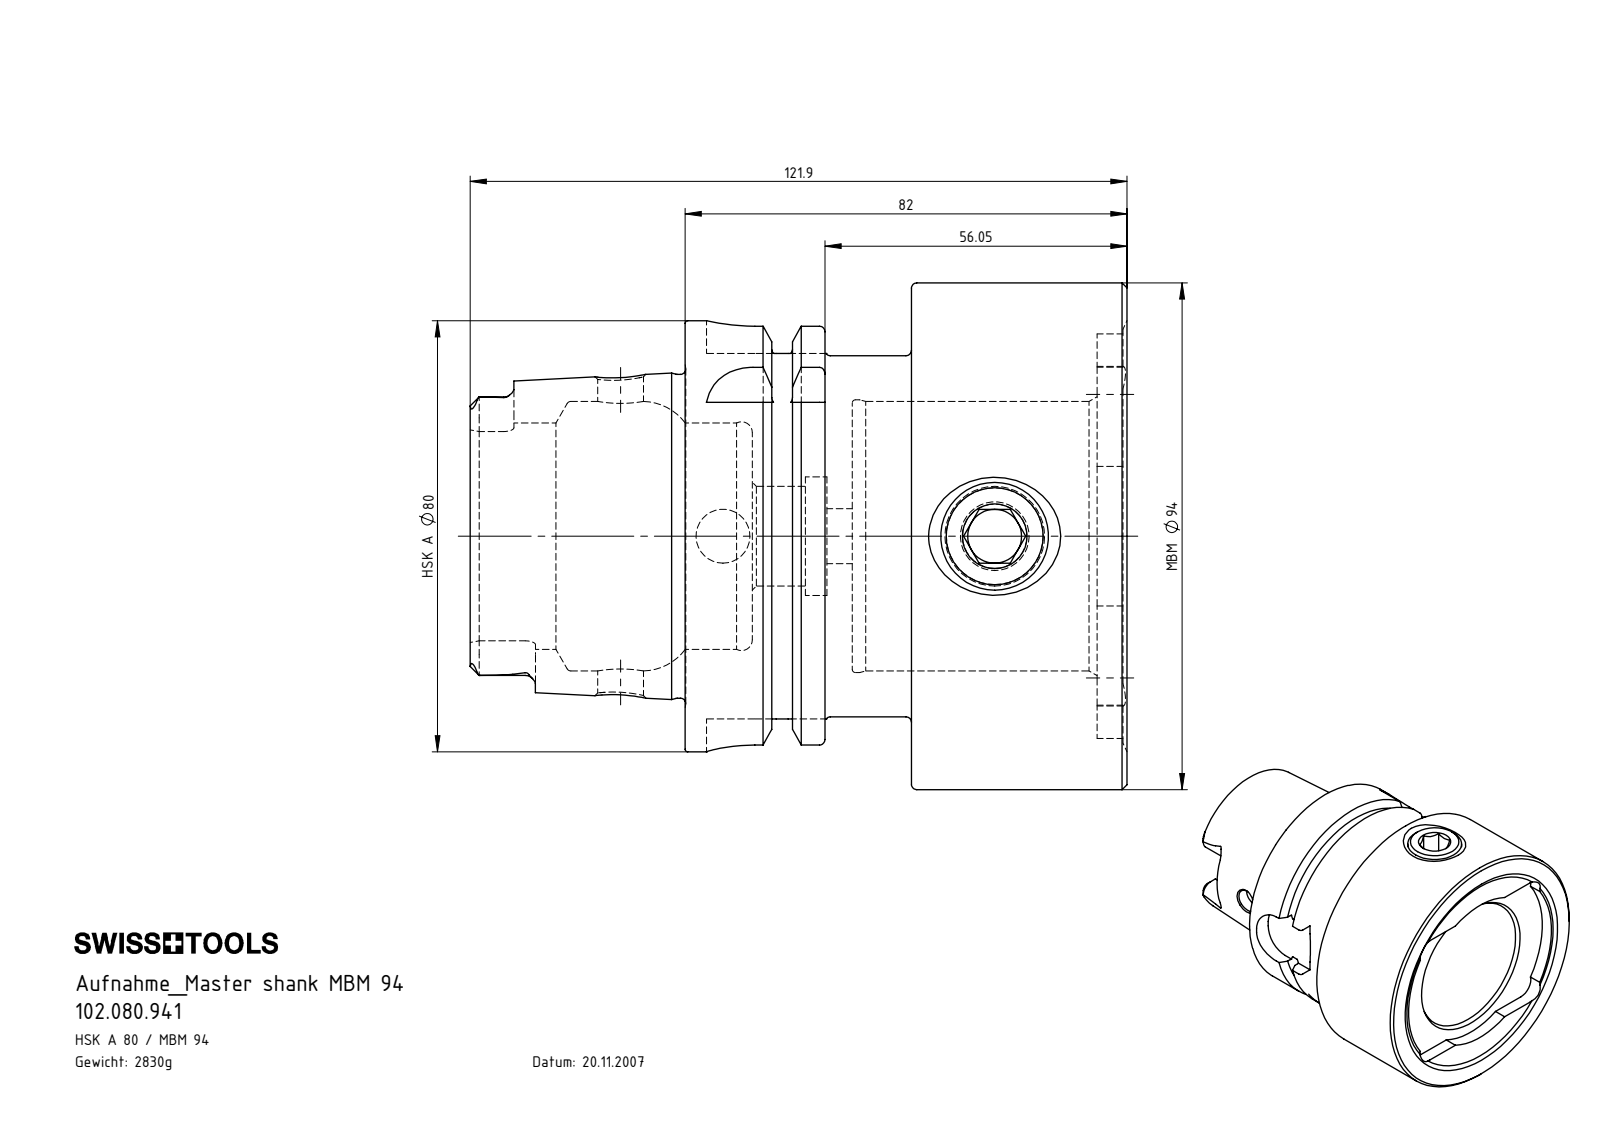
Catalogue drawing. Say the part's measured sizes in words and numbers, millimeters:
The part is named "102.080.941; MB9-ER1.001.032_A; HA8-MB9.K01.082_B_Fertigbearbeitung". Its 3-D file was written by "SolidWorks 2017 (CONFIG_CONTROL_DESIGN)". It is 2 solids with 230 faces: 72 planar, 69 cylindrical and 89 other. Overall it measures 121.9 by 94 by 94 millimeters. Its volume is 360 446 cubic millimeters and its surface area 66 438 square millimeters. Round holes: 2 of diameter 10, 2 of diameter 18.5, 1 of diameter 8.5, 1 of diameter 10.2, 1 of diameter 22, 1 of diameter 42, 1 of diameter 50, 1 of diameter 50.6. Round bosses or shafts: 1 of diameter 94, 1 of diameter 80, 1 of diameter 69.95, 1 of diameter 67, 1 of diameter 60.06, 1 of diameter 20. Partial cylindrical surfaces (rounded edges, fillets, slot ends): 6 of radius 1.9, 4 of radius 3.88, 4 of radius 5.2, 4 of radius 9, 1 of radius 30, 1 of radius 37.52. The main face-to-face distances are 11, 31, 42, 76.45, 45.45, 34.45, 82, 51, 40, 5.55. The hole center spacings are 50.45.
